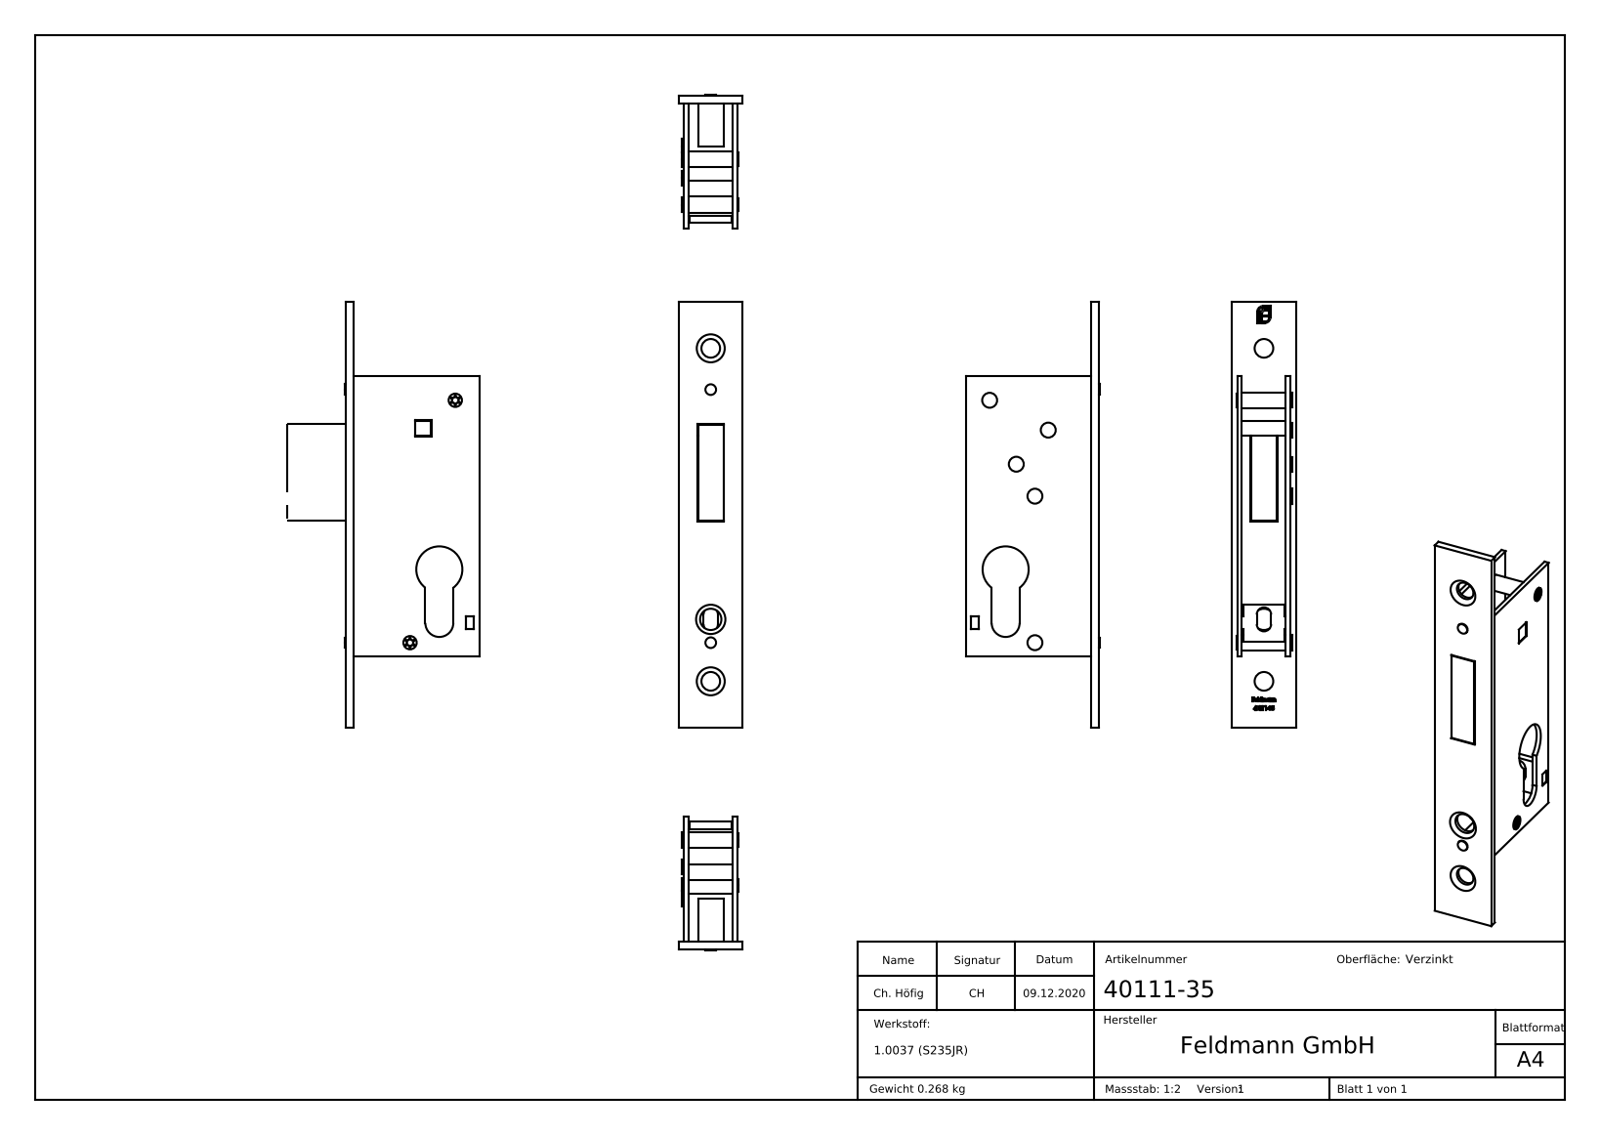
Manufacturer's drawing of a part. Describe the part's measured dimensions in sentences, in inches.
The part is named "40111-35". Its 3-D file was written by "SolidWorks 2018 (CONFIG_CONTROL_DESIGN)". It is 3 solids with 414 faces: 238 planar, 71 cylindrical and 105 other. Overall it measures 6.299 by 1.984 by 0.945 inches. Its volume is 2.097 cubic inches and its surface area 48.15 square inches. Round holes: 2 of diameter 0.276, 1 of diameter 0.315. Round bosses or shafts: 5 of diameter 0.22, 2 of diameter 0.236, 2 of diameter 0.197, 2 of diameter 0.157. Partial cylindrical surfaces (rounded edges, fillets, slot ends): 12 of radius 0.006, 12 of radius 0.02, 2 of radius 0.106, 1 of radius 0.207, 1 of radius 0.341. The main face-to-face distances are 0.719, 0.069, 0.65, 0.787, 0.118, 0.512, 0.207, 0.581, 0.138, 0.797. The hole center spacings are 0.915, 4.006, 4.921.
